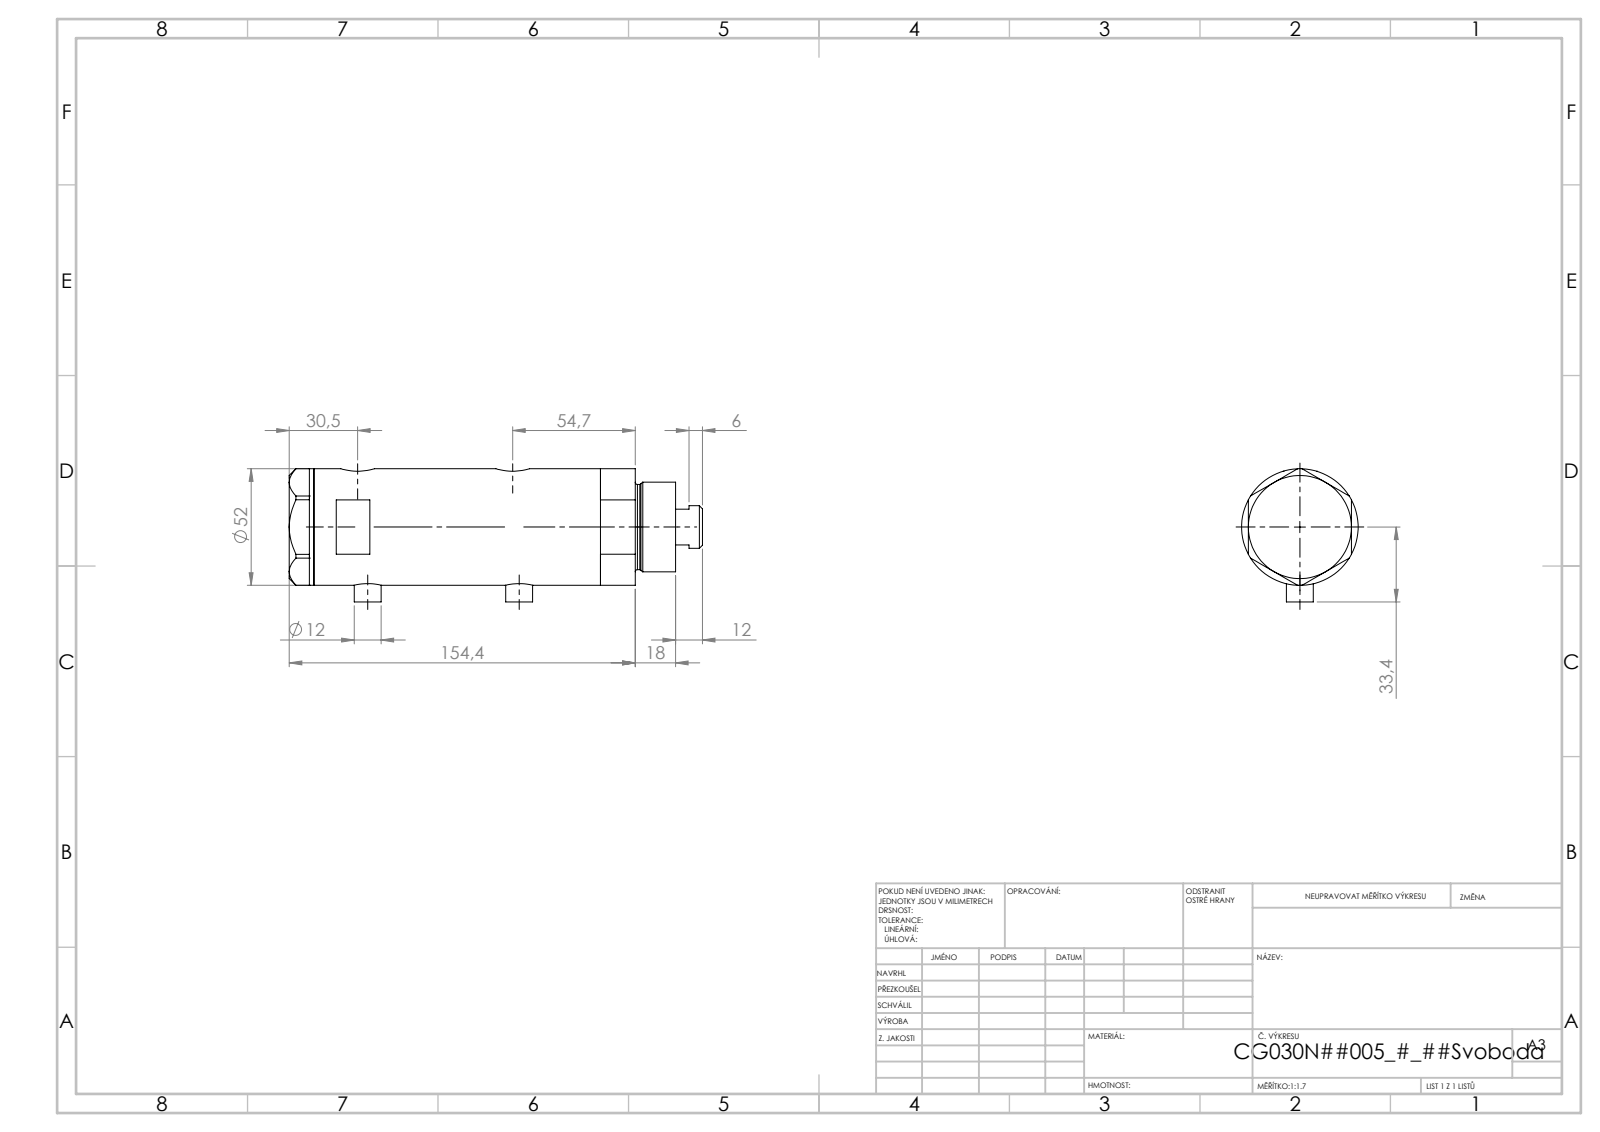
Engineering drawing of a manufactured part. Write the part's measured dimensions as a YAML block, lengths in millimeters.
part_name: "V270CG_BACK; V270CG_FRONT; V270CG_MIDDLE; V270CG_VC"
step_written_by: "SolidWorks 2019 (CONFIG_CONTROL_DESIGN)"
units: millimeters
bodies: {solids: 4, faces: 140, planar: 67, cylindrical: 53, other: 20}
overall_size: [184.4, 59.4, 52]
volume: 344098
surface_area: 78312
round_holes:
  - {diameter: 5, count: 2}
  - {diameter: 9.73, count: 2}
  - {diameter: 12.5, count: 2}
  - {diameter: 15, count: 2}
  - {diameter: 6.5, count: 1}
  - {diameter: 20, count: 1}
  - {diameter: 21.5, count: 1}
  - {diameter: 30, count: 1}
  - {diameter: 33, count: 1}
  - {diameter: 44, count: 1}
round_bosses_or_shafts:
  - {diameter: 12, count: 2}
  - {diameter: 52, count: 1}
  - {diameter: 40, count: 1}
  - {diameter: 38, count: 1}
  - {diameter: 19, count: 1}
face_to_face_distances: [91.5, 23.8, 67.7, 11, 34.8, 102.5, 46, 138.9, 127.9, 104.1]
hole_center_spacings: [2.9, 4.5, 64.7, 67.6, 69.2, 72.1]
